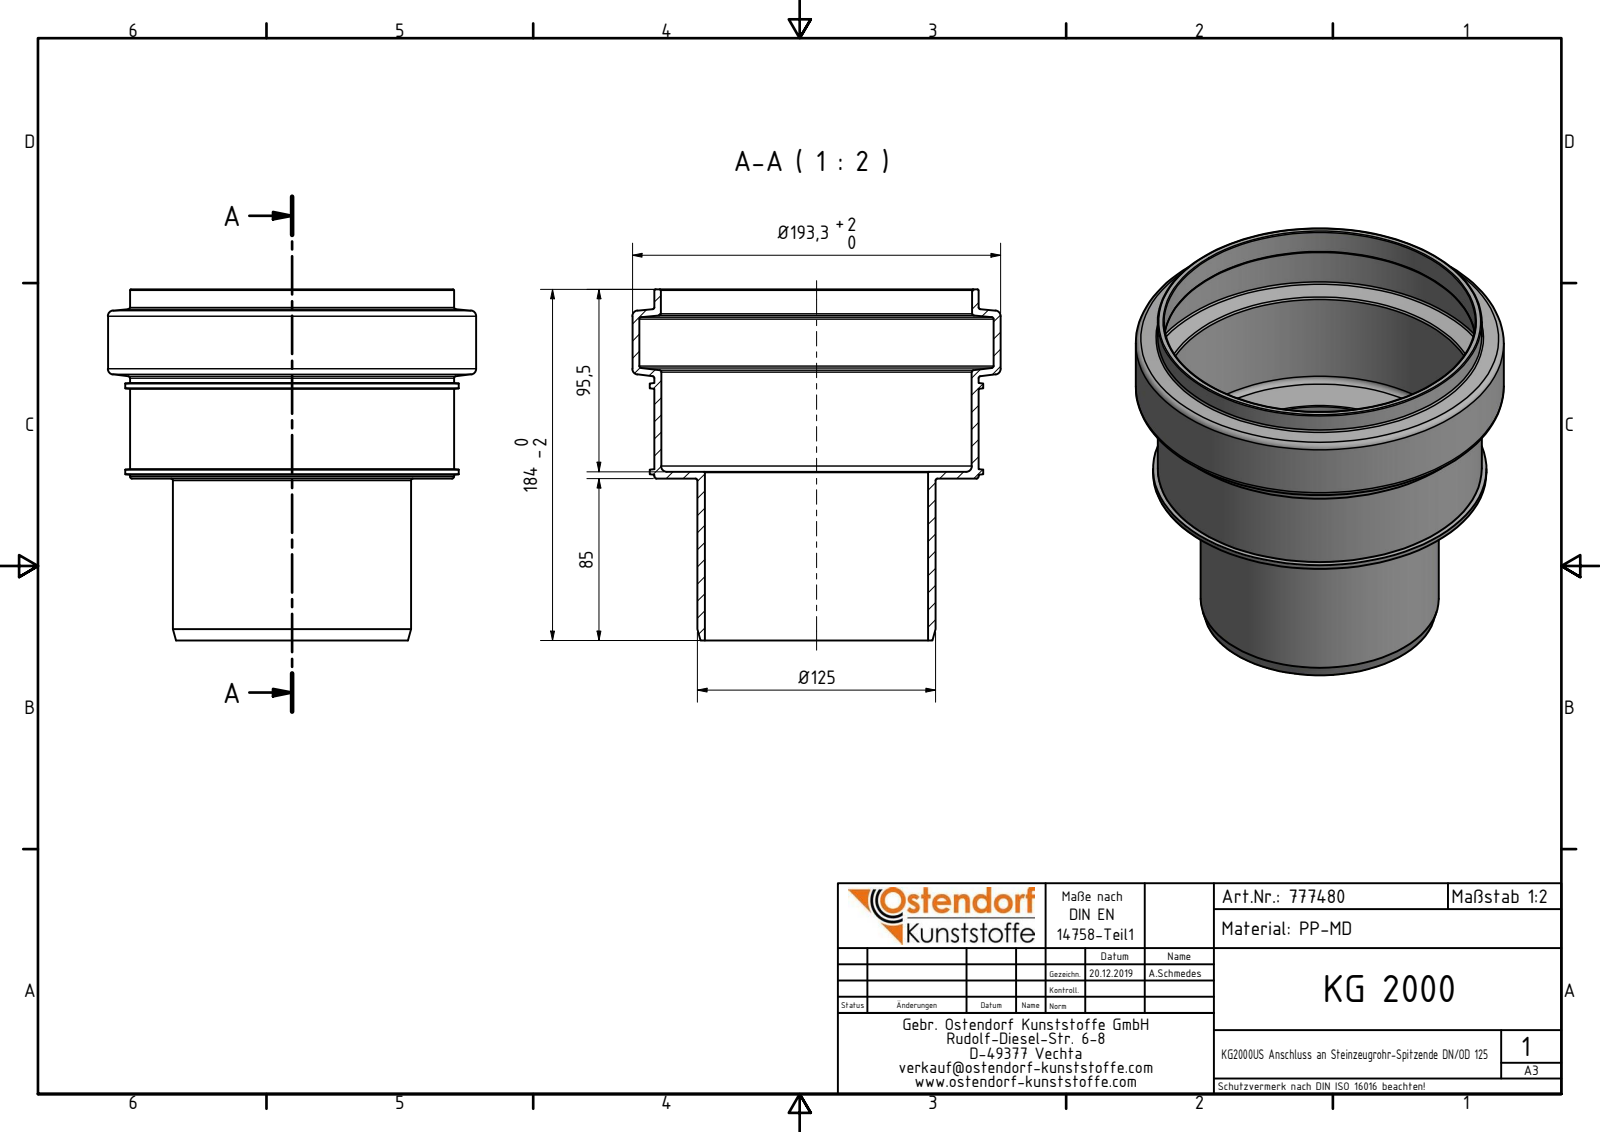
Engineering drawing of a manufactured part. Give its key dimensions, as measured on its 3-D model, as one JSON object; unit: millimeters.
{"part_name": "777480 KG2000US Anschluss an Steinzeugrohr- Spitzende DN125", "step_written_by": "Autodesk Inventor 2020 (AUTOMOTIVE_DESIGN)", "units": "millimeters", "bodies": {"solids": 1, "faces": 39, "planar": 4, "cylindrical": 12, "other": 23}, "overall_size": [193.3, 193.3, 184.3], "volume_mm3": 401977, "surface_area_mm2": 220273, "round_holes": [[117.19, 1], [163.01, 1], [163.56, 1], [186.11, 1]], "round_bosses_or_shafts": [[193.3, 1], [175.11, 1], [170.2, 1], [125, 1]], "face_to_face_distances": [3.6, 95.7, 99.3, 184.3, 88.6, 85]}
